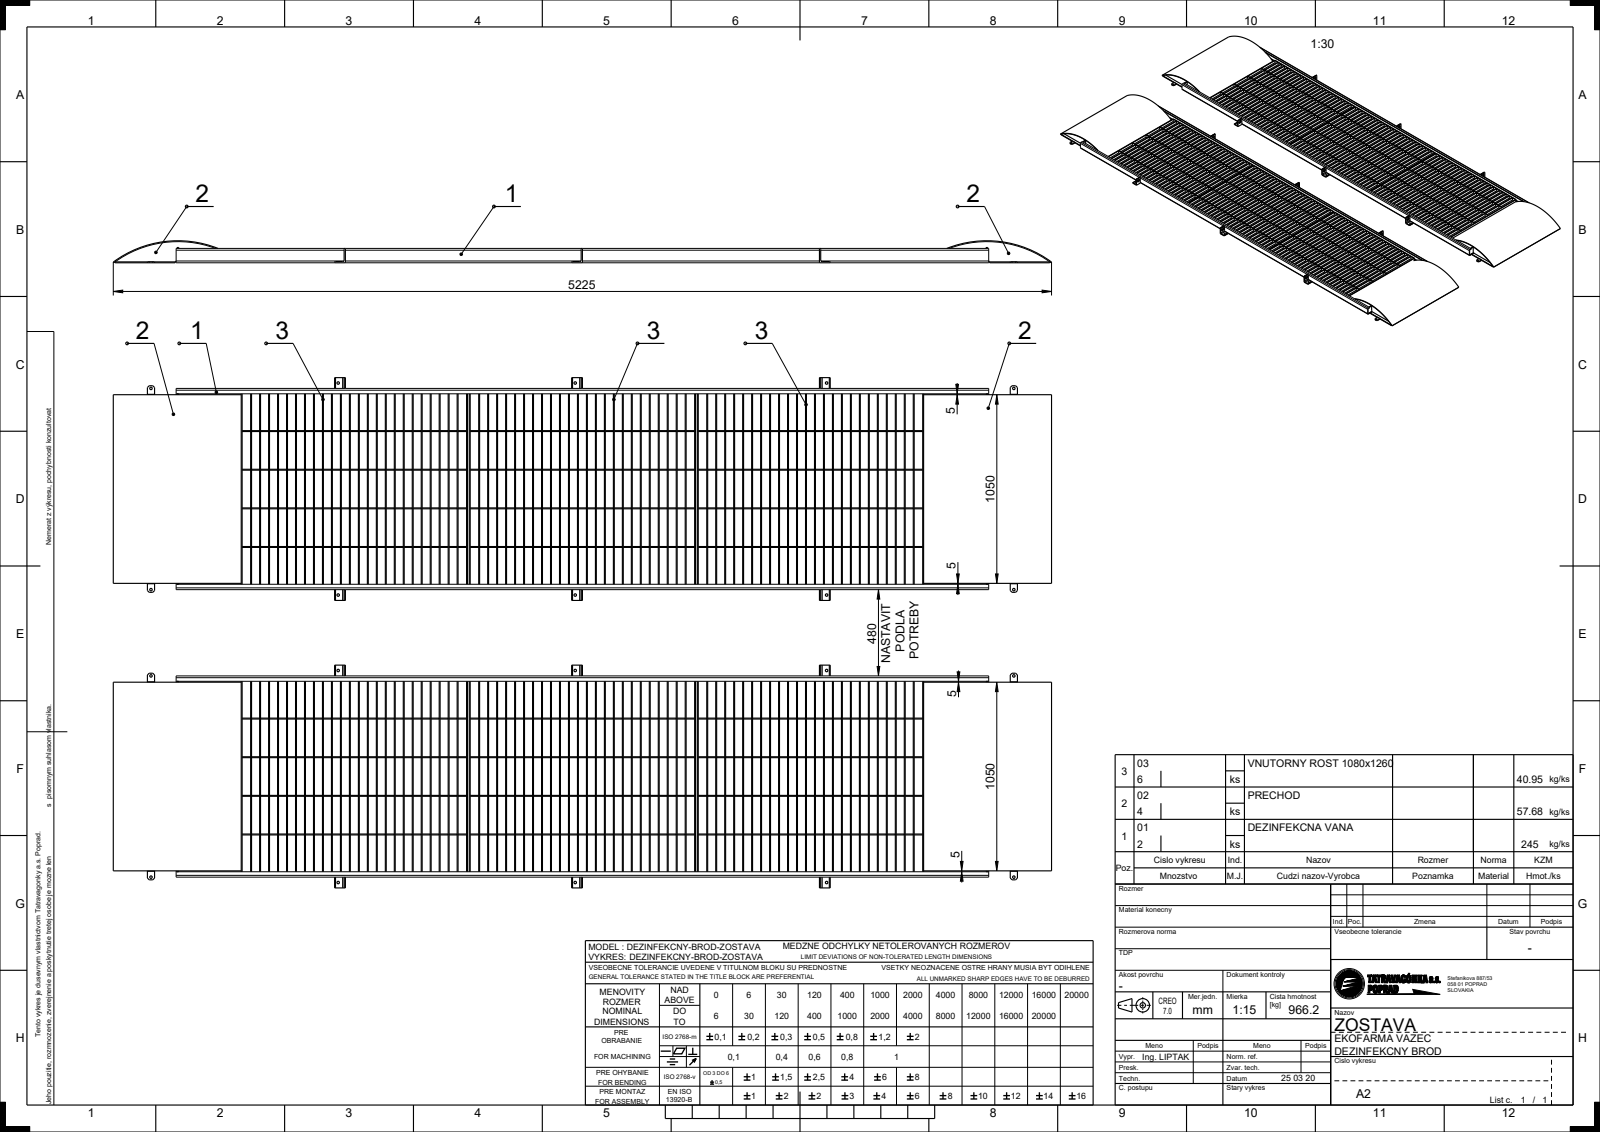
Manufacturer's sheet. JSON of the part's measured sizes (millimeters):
{"part_name": "VANA-01; ZASLEPKA-01; L80X60X7X60_EN10056_UPR; 01_DEZINFEKCNA-VANA_ASM (+8 more)", "step_written_by": "CREO PARAMETRIC BY PTC INC, 2020454 (CONFIG_CONTROL_DESIGN)", "units": "millimeters", "bodies": {"solids": 286, "faces": 8589, "planar": 7421, "cylindrical": 682, "other": 486}, "overall_size": [20398.03, 4020.1, 3118.34], "volume_mm3": 13410000000, "surface_area_mm2": 358700000, "round_holes": [[14, 20], [600, 5], [30, 4], [5, 1], [10, 1], [285, 1], [320, 1]], "round_bosses_or_shafts": [[75, 8], [1050, 6], [200, 6], [100, 6], [300, 4], [25, 4], [135.57, 2], [32.01, 2]], "partial_cylinders_radius": [[40, 28], [1, 20], [35, 20], [30, 18], [0.5, 16], [5, 16], [10, 14], [1.5, 13]], "face_to_face_distances": [130, 1165, 1295, 5, 400, 795, 50, 370, 1680, 1170], "hole_center_spacings": [1600, 1042.93, 1180, 1552.19, 3762.62, 3934.32, 2720, 420]}
